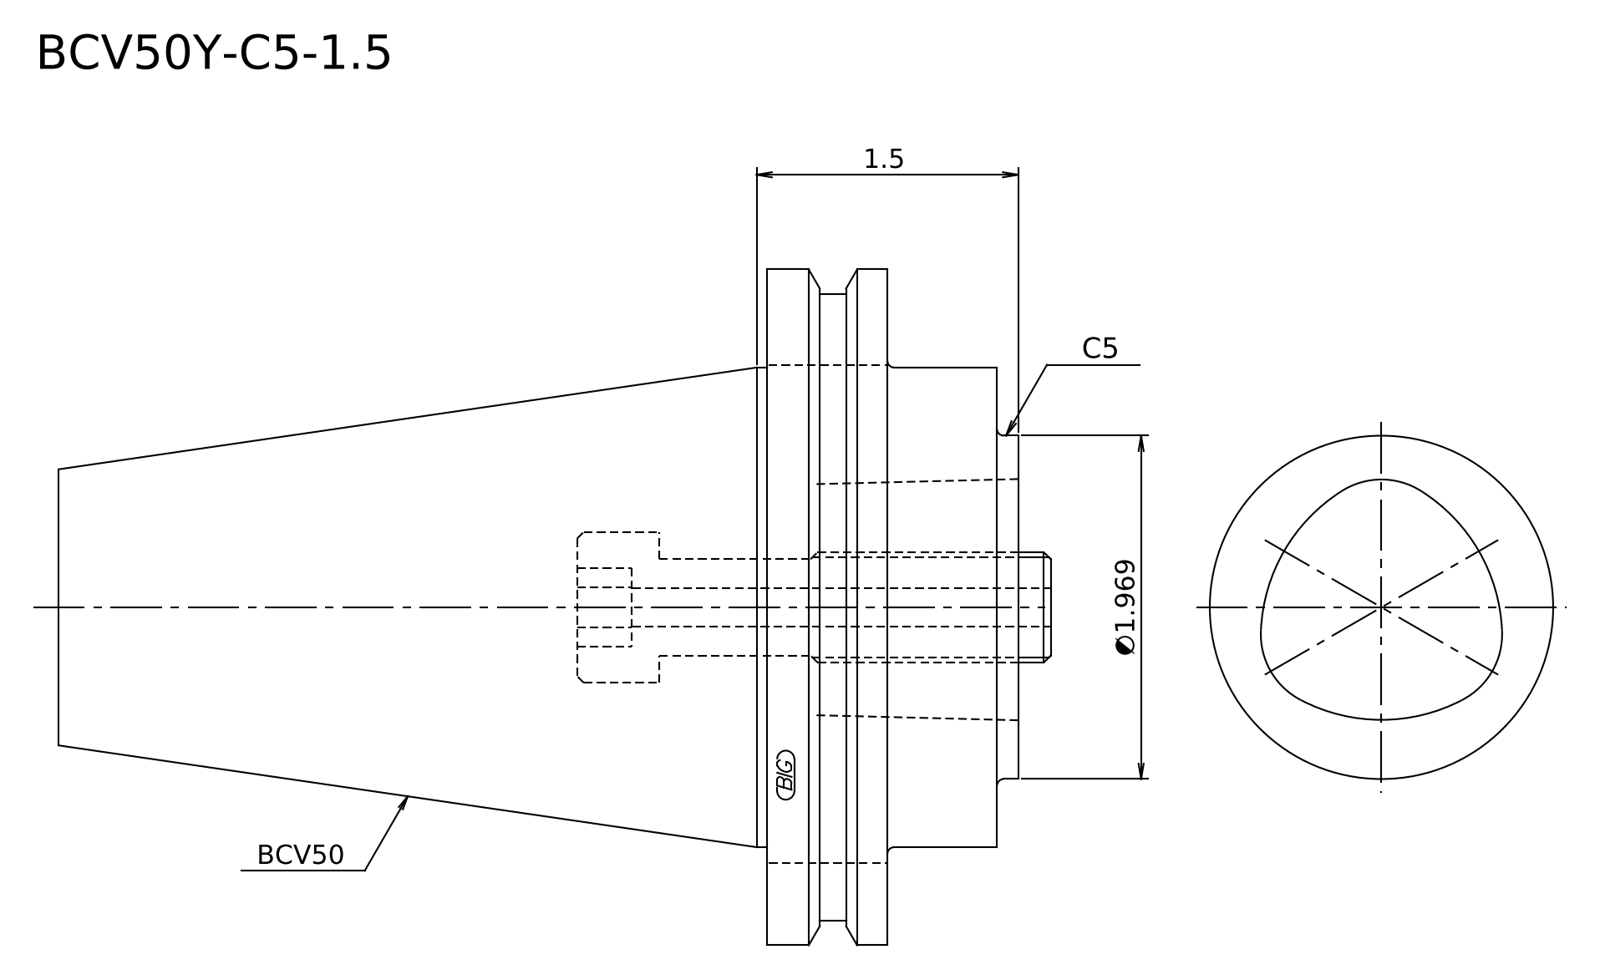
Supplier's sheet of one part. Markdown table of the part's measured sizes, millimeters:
| quantity | value |
| --- | --- |
| STEP written by | Kubotek KeyCreator 2011 V10.0.2 (22737) (automotive_design) |
| units | millimeters |
| bodies | 1 solid, 18 faces (7 planar, 6 cylindrical, 5 other) |
| overall size | 139.7 × 98.42 × 98.42 |
| volume | 448 755 mm³ |
| surface area | 41 238 mm² |
| round bosses / shafts (diameter × count) | 98.42 × 1, 91.29 × 1, 69.85 × 1, 50 × 1 |
| main face-to-face distances | 17.55, 19.05, 36.6, 3.1, 15.95, 33.5, 139.7, 136.6, 120.65, 103.1 |
